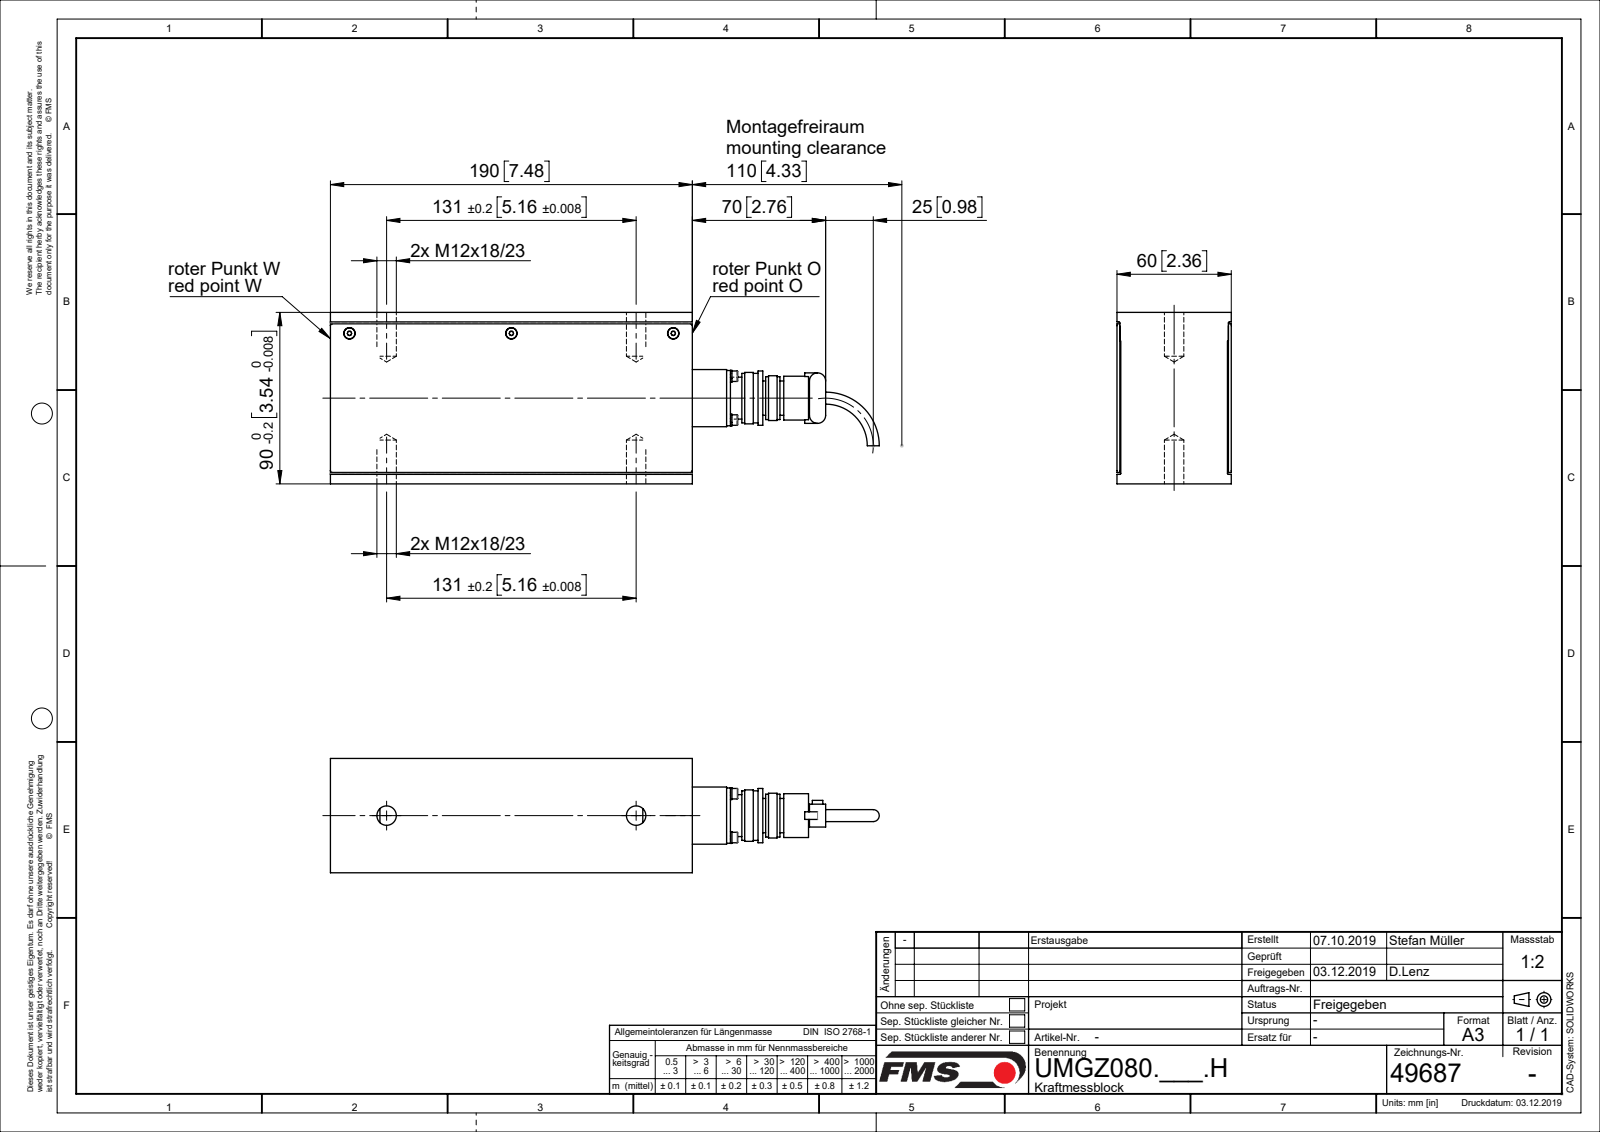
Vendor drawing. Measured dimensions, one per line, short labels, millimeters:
name: U49687; U4963504; U49541; L49026 (+6 more)
written by: Mechanical Desktop 2007 (CONFIG_CONTROL_DESIGN)
unit: mm
bodies: 19 solids, 382 faces (134 planar, 162 cylindrical, 86 other)
size: 310.5 × 95 × 60
volume: 1 041 000 mm³; area: 151 297 mm²
holes: 7× ⌀2.6, 4× ⌀3.2, 4× ⌀3.4, 3× ⌀6, 2× ⌀10.44, 1× ⌀23
bosses: 7× ⌀3, 4× ⌀6.2, 4× ⌀5.5, 4× ⌀2.5, 1× ⌀28, 1× ⌀22, 1× ⌀21, 1× ⌀20
rounds: 4× R1, 4× R4
face distances: 1.5, 58.5, 2, 58, 0.5, 56.5, 60, 57, 56, 90
hole spacings: 16.26, 23, 32.53, 85, 131, 170
